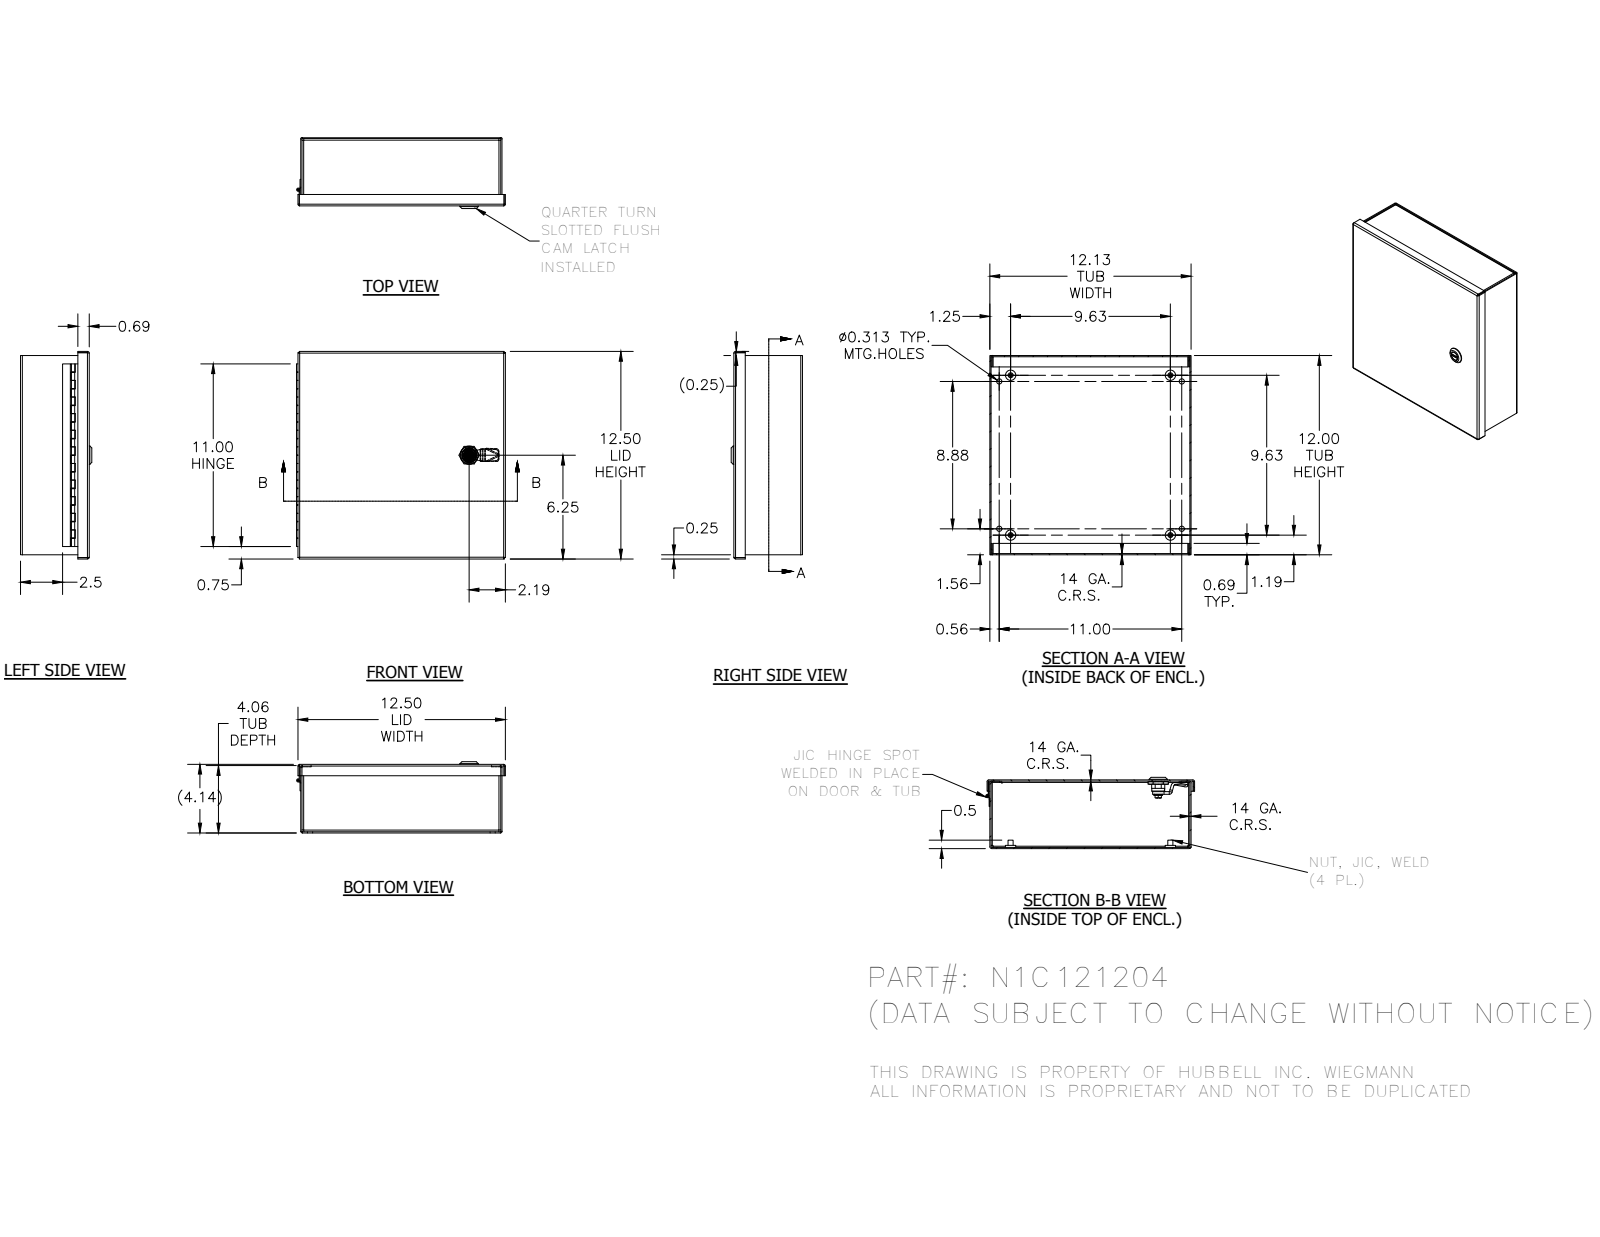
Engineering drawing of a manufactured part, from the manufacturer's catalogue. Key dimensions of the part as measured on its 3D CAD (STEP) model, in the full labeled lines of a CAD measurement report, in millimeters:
Part name (STEP PRODUCT): N1C_SMALL; N1C1204TB; N1C121204BLR; HFW3513 (+8 more)
STEP written by: Autodesk Inventor 2012 (AUTOMOTIVE_DESIGN)
Units: millimetres
Bodies: 19 solids, 715 faces (411 planar, 222 cylindrical, 82 other)
Overall size (bounding box): 319.6 × 317.5 × 109.1
Volume: 720 000 mm³ · Surface area: 785 200 mm²
Round holes (diameter × count): ⌀4 ×4, ⌀8 ×4, ⌀2.9 ×1, ⌀5 ×1, ⌀8 ×1, ⌀10 ×1, ⌀10.2 ×1, ⌀16.1 ×1, ⌀20.4 ×1
Round bosses / shafts (diameter × count): ⌀15.9 ×4, ⌀7.6 ×4, ⌀28 ×1, ⌀22 ×1, ⌀19.8 ×1, ⌀16 ×1, ⌀15.2 ×1, ⌀13.5 ×1
Partial cylindrical surfaces — rounded edges, fillets, slot ends (radius × count): R0.3 ×30, R0.8 ×16, R2.7 ×16, R0.5 ×10, R4 ×4, R0.4 ×3, R1 ×1, R4.4 ×1
Main face-to-face distances: 1.9, 103.2, 101.3, 105.1, 306.1, 302.9, 304.2, 3.8, 308, 304.8
Hole centre spacings: 19.9, 235.6, 244.5, 262.1, 351.9, 118.3, 123.6, 225.4
